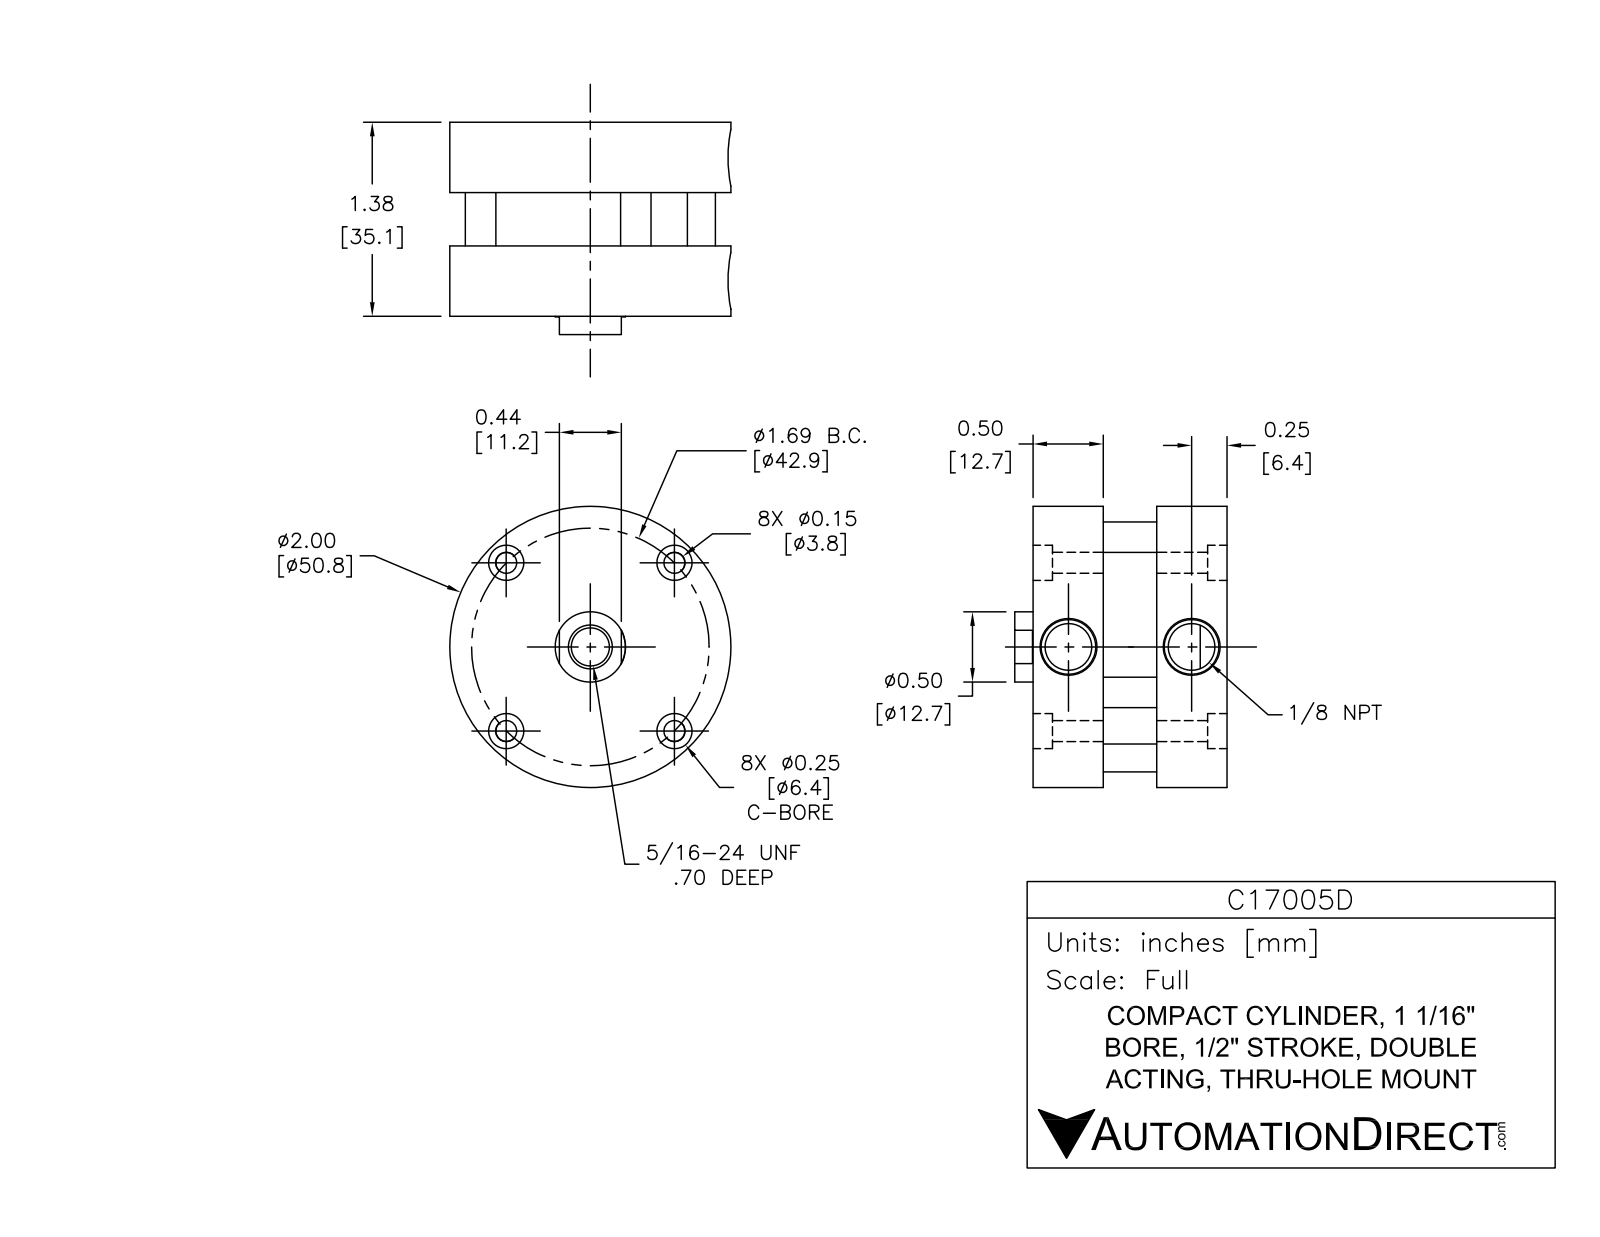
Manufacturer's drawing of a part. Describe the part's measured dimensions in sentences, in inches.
The part is named "C17005D-FO1_BM_r; C17005D-FO1_BM_heads; C17005D-FO1_BM_tube; C17005D (+3 more)". Its 3-D file was written by "SolidWorks 2014 (AUTOMOTIVE_DESIGN)". It is 9 solids with 165 faces: 49 planar, 98 cylindrical and 18 other. Overall it measures 2 by 2 by 1.51 inches. Its volume is 3.053 cubic inches and its surface area 38.12 square inches. Round holes: 4 of diameter 0.136, 4 of diameter 0.156, 4 of diameter 0.25, 2 of diameter 0.125, 1 of diameter 0.267, 1 of diameter 0.5, 1 of diameter 0.502, 1 of diameter 1.062, 1 of diameter 1.122. Round bosses or shafts: 4 of diameter 0.272, 1 of diameter 2. The main face-to-face distances are 0.5, 0.88, 0.282, 0.598, 1.098, 0.218, 1.38, 0.38, 0.816, 0.316. The hole center spacings are 0.33, 0.845, 0.845, 0.939, 1.195, 1.195, 1.406, 1.657.
